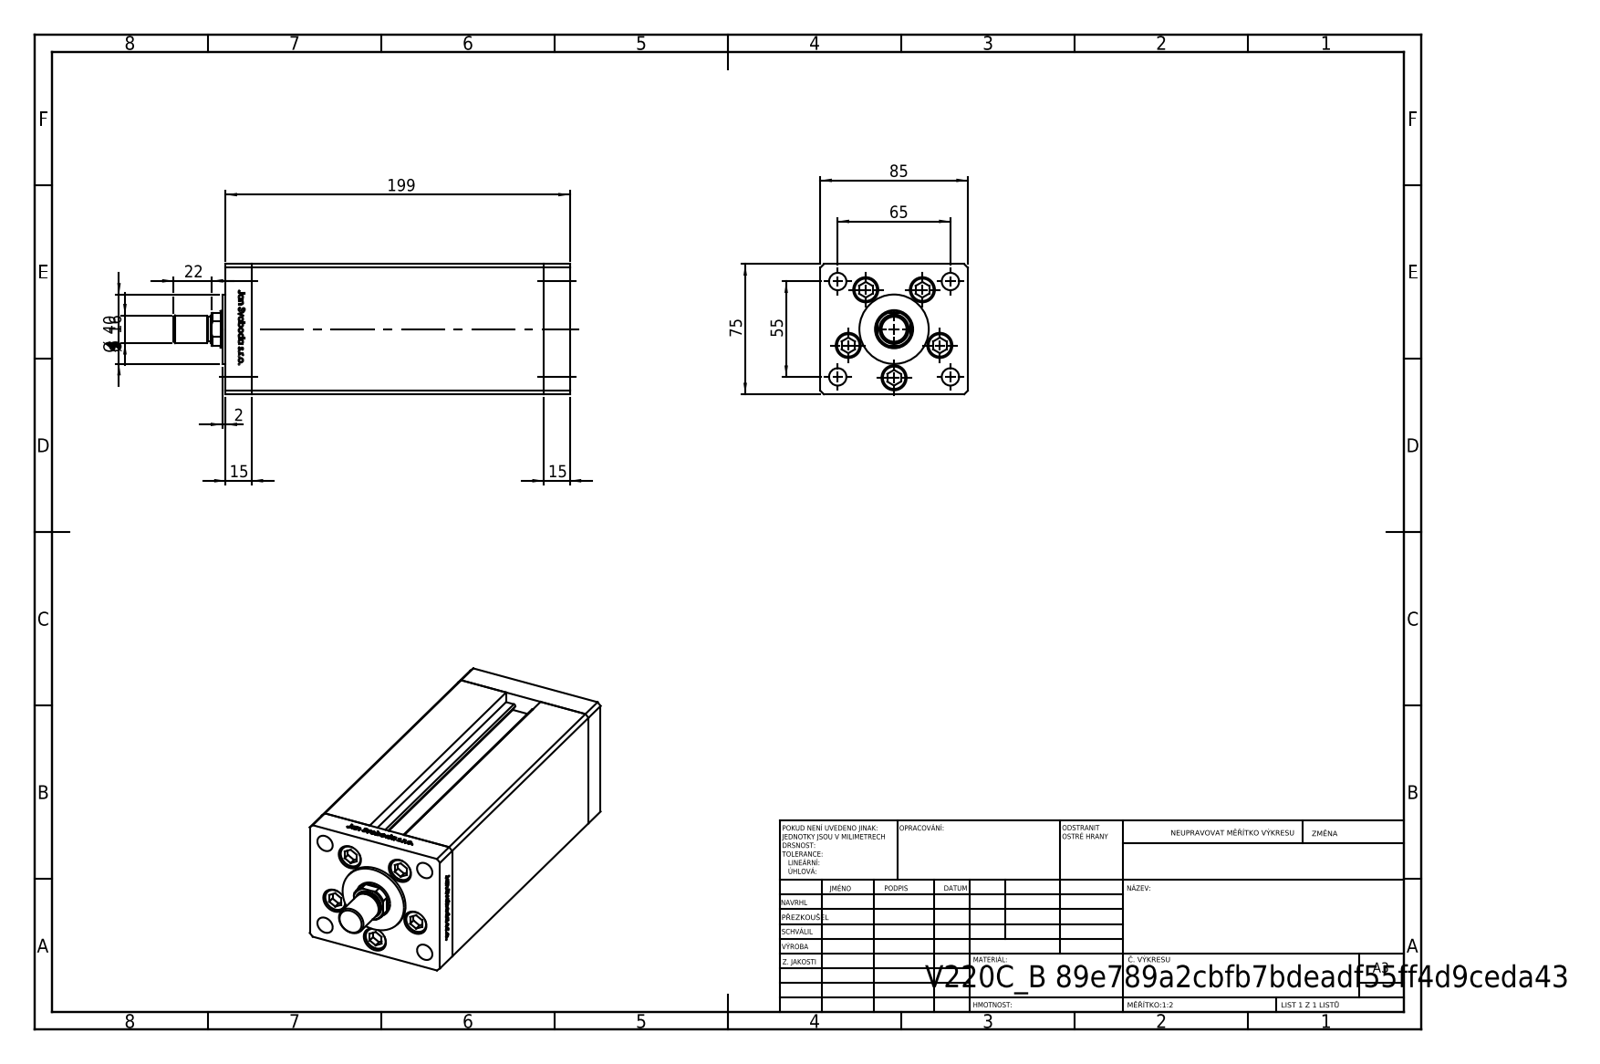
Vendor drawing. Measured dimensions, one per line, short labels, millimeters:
name: ALLEN BOLT; V220C_FRONT_B; V220C_B_VC; V220C BACK_B (+2 more)
written by: SolidWorks 2019 (CONFIG_CONTROL_DESIGN)
unit: mm
bodies: 15 solids, 1191 faces (466 planar, 147 cylindrical, 578 other)
size: 228.5 × 85 × 75
volume: 1 120 000 mm³; area: 170 474 mm²
holes: 5× ⌀11, 5× ⌀14.5, 4× ⌀10, 2× ⌀2, 2× ⌀13.16, 1× ⌀15, 1× ⌀22
bosses: 5× ⌀8, 1× ⌀40, 1× ⌀16, 1× ⌀14
rounds: 2× R0.93, 1× R10.5
face distances: 85, 75, 168.5, 15, 183.5, 198.5, 68.5, 64.5, 10.5, 9
hole spacings: 28, 42.57, 16.86, 19.17, 32.33, 32.5, 33.63, 37.33
